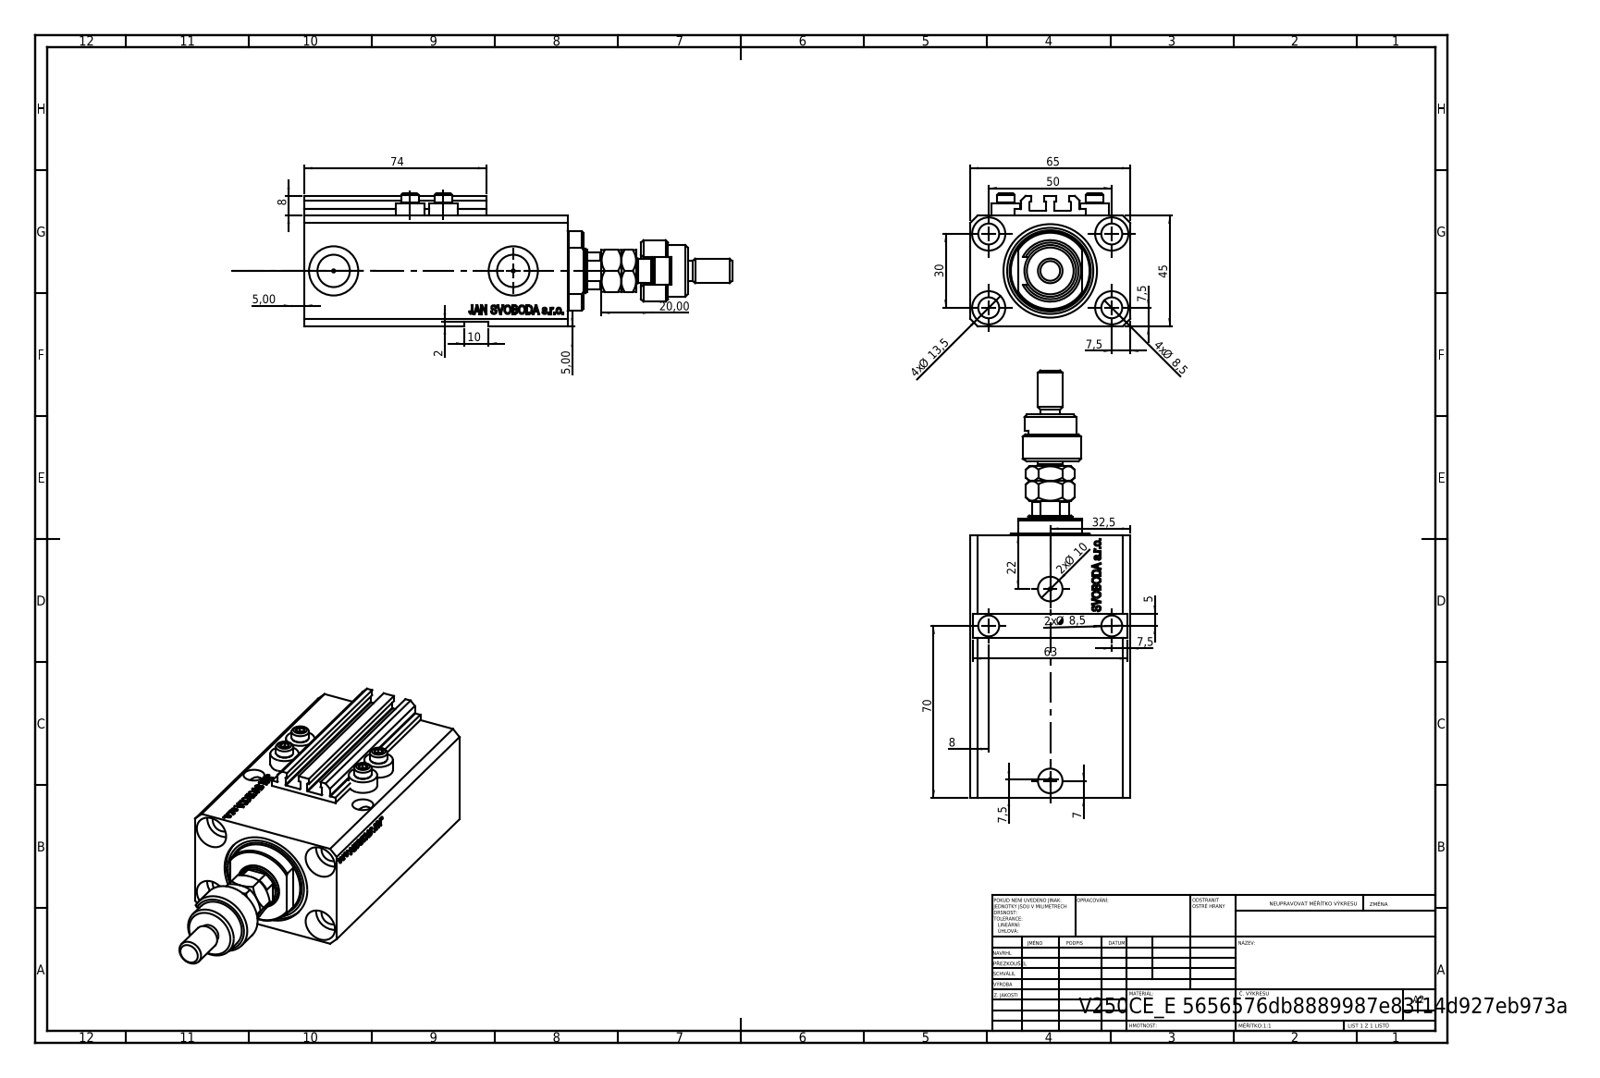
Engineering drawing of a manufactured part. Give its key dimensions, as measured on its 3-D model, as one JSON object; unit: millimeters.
{"part_name": "ALLEN BOLT V250CE; V250CE_E_Body; V250CE_C_VCP; MFA (+2 more)", "step_written_by": "SolidWorks 2019 (CONFIG_CONTROL_DESIGN)", "units": "millimeters", "bodies": {"solids": 10, "faces": 1152, "planar": 539, "cylindrical": 139, "other": 474}, "overall_size": [173.9, 65, 54], "volume_mm3": 288654, "surface_area_mm2": 83406, "round_holes": [[8.5, 7], [1.25, 4], [4, 4], [13.5, 4], [10, 2], [13.16, 2], [20, 2], [18, 1], [38, 1]], "round_bosses_or_shafts": [[11.6, 4], [7, 4], [25, 1], [21, 1], [16, 1], [10, 1], [8, 1]], "partial_cylinders_radius": [[0.2, 10], [5.5, 1], [8.5, 1], [8.75, 1], [16, 1]], "face_to_face_distances": [45, 65, 2, 81.9, 47, 107, 25.1, 2.5, 6.9, 75], "hole_center_spacings": [29.15, 50, 13.6, 15.12, 27.89, 30, 33.62, 36]}
